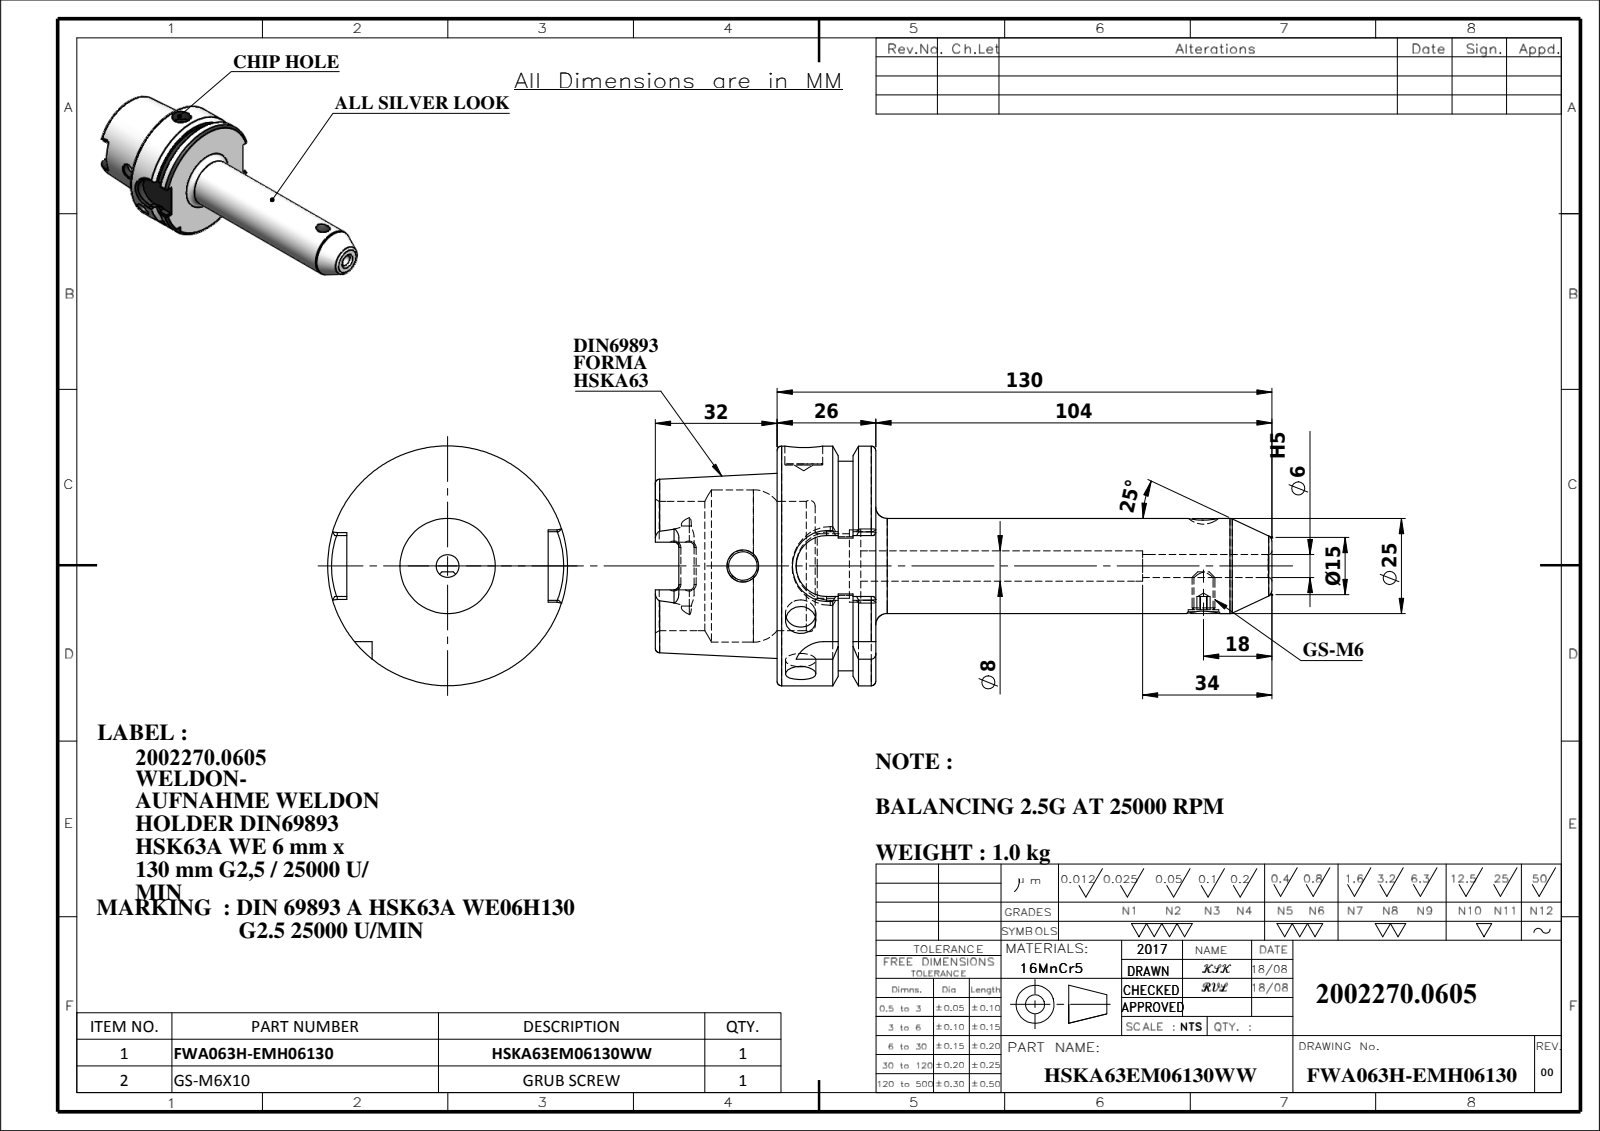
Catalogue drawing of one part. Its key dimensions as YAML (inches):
part_name: "HSKA63EM06130WW; GS-M6X10-DIN1835-B; 9163A-WE806130"
step_written_by: "SolidWorks 2018 (CONFIG_CONTROL_DESIGN)"
units: inches
bodies: {solids: 2, faces: 198, planar: 65, cylindrical: 55, other: 78}
overall_size: [6.378, 2.48, 2.48]
volume: 7.673
surface_area: 50.85
round_holes:
  - {diameter: 0.315, count: 4}
  - {diameter: 0.197, count: 1}
  - {diameter: 0.236, count: 1}
  - {diameter: 0.295, count: 1}
  - {diameter: 0.394, count: 1}
  - {diameter: 0.669, count: 1}
  - {diameter: 0.748, count: 1}
  - {diameter: 1.339, count: 1}
  - {diameter: 1.575, count: 1}
round_bosses_or_shafts:
  - {diameter: 2.48, count: 1}
  - {diameter: 2.165, count: 1}
  - {diameter: 0.984, count: 1}
  - {diameter: 0.236, count: 1}
partial_cylinders:
  - {radius: 0.051, count: 6}
  - {radius: 0.113, count: 4}
  - {radius: 0.315, count: 2}
  - {radius: 0.354, count: 1}
face_to_face_distances: [1.022, 0.394, 0.628, 1.26, 1.654, 2.281, 2.083, 2.126, 0.866, 0.472]
hole_center_spacings: [4.134]
